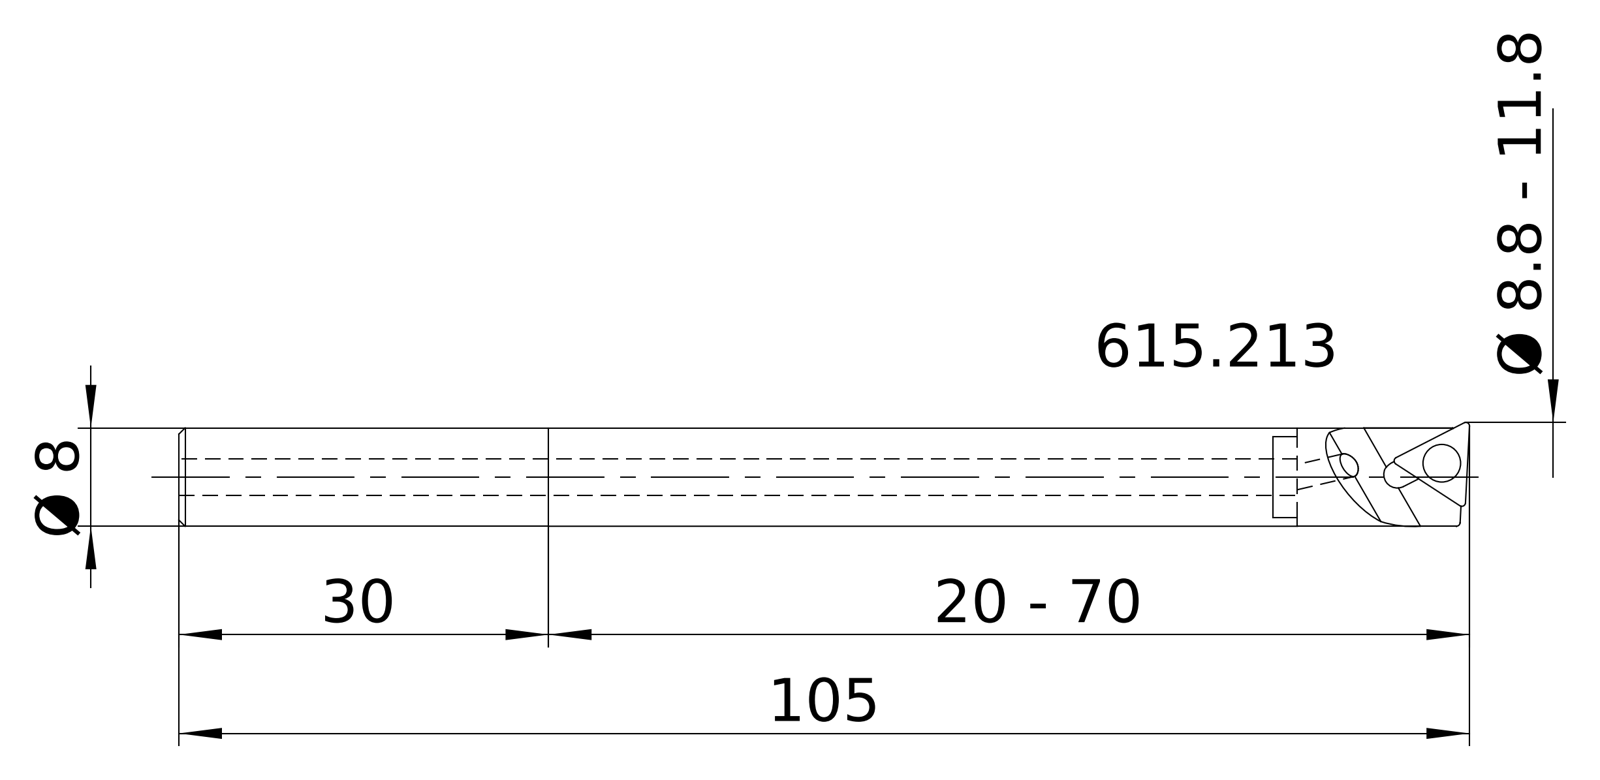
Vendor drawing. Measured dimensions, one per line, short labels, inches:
name: 615.213 Kaiser E9 TP07 x 105HM|694.103 Kaiser ETL M2x4.8 T6 IP 10S;Kreismuster1; 615.213 Kaiser E9 TP07 x 105HM|651.735 Kaiser TPGT 070203 K10C;Kombinieren1; 615.213 Kaiser E9 TP07 x 105HM|615.213 Kaiser E9 TP07 x 105HM;Schnitt-Rotation1
written by: ACIS (automotive_design)
unit: in
bodies: 3 solids, 82 faces (19 planar, 33 cylindrical, 30 other)
size: 4.053 × 0.333 × 0.315
volume: 0.282 in³; area: 5.214 in²
holes: 1× ⌀0.061, 1× ⌀0.079, 1× ⌀0.091
bosses: 1× ⌀0.315, 1× ⌀0.106, 1× ⌀0.079
rounds: 6× R0.006, 6× R0.012, 1× R0.043, 1× R0.118
face distances: 0.098, 0.11, 0.087, 0.03, 0.019, 0.08, 0.189, 0.178, 0.159, 0.079
